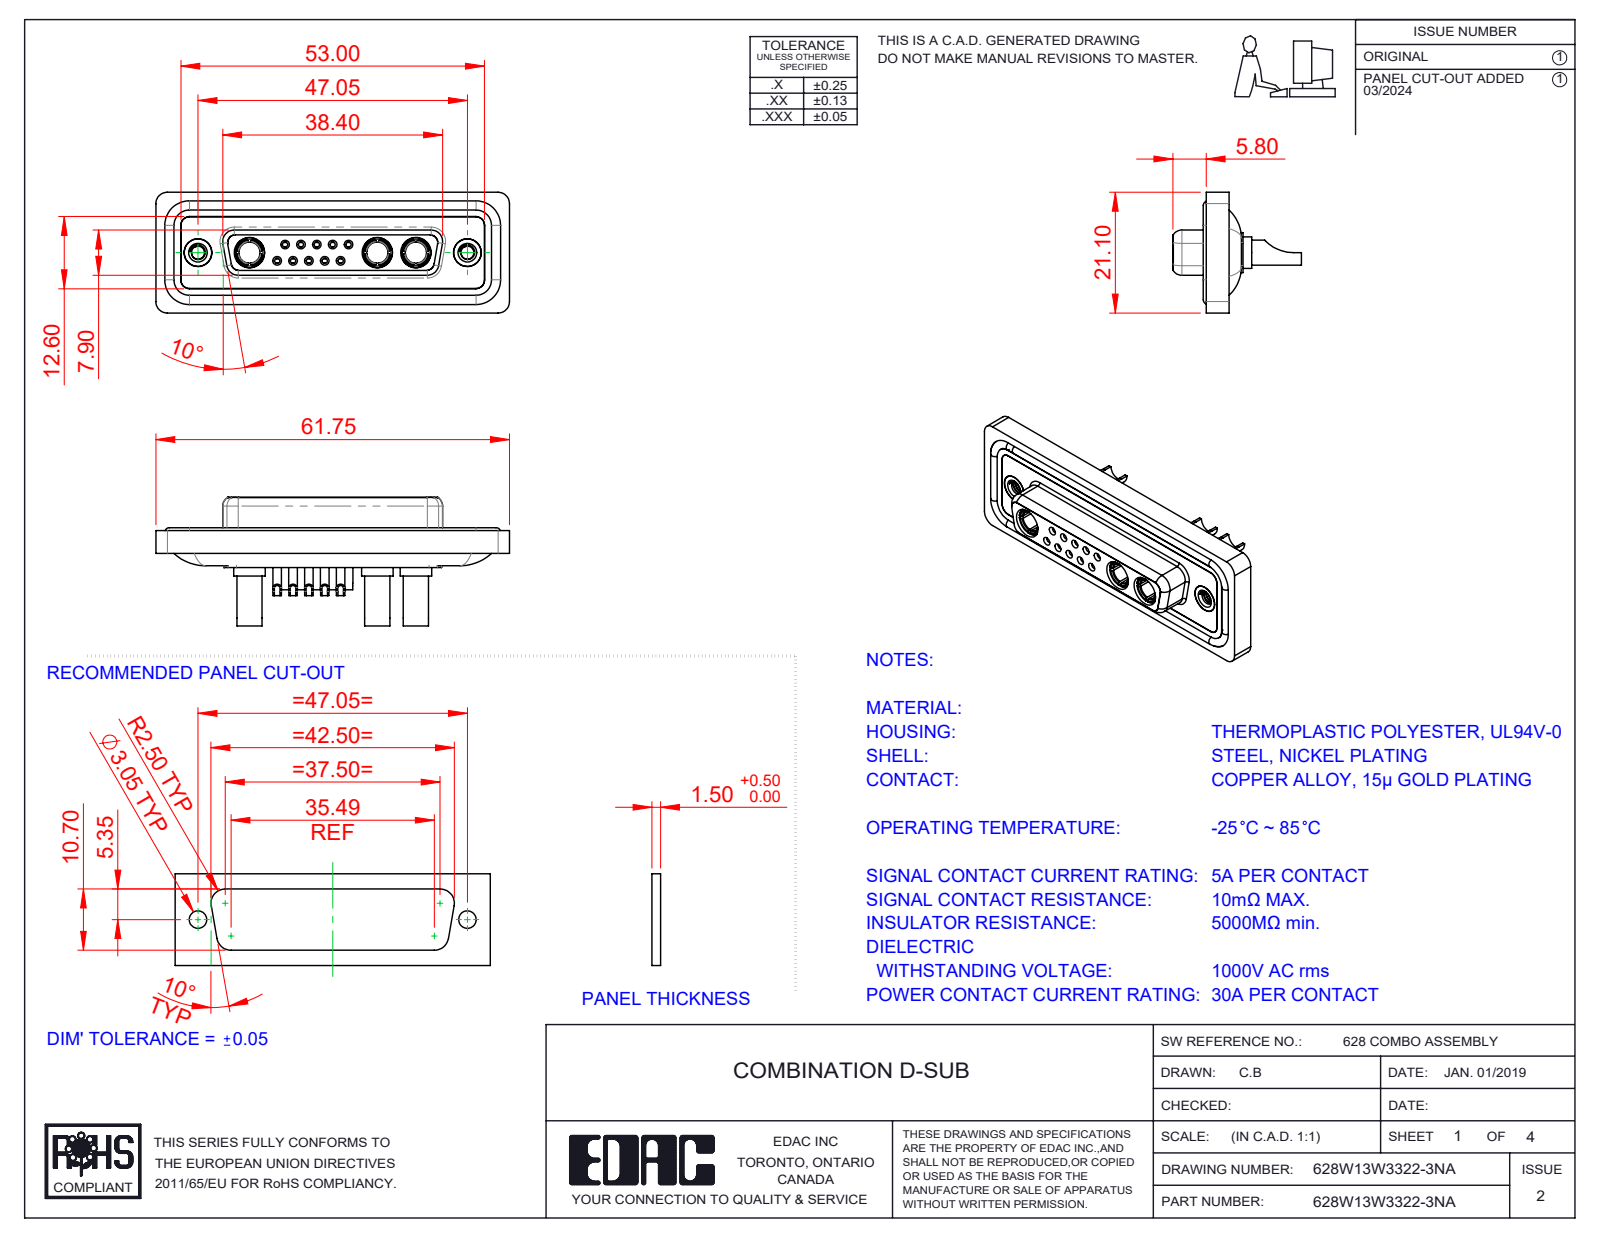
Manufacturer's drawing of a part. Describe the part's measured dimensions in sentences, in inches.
The part is named "628Combo Shell Rear_25 Contacts; Power Socket_30A SC; 628Combo Contact Row 1_22; 628Combo Housing_13W3 (+5 more)". Its 3-D file was written by "SolidWorks 2023 (CONFIG_CONTROL_DESIGN)". It is 23 solids with 1174 faces: 371 planar, 478 cylindrical and 325 other. Overall it measures 2.431 by 0.884 by 0.831 inches. Its volume is 0.511 cubic inches and its surface area 21.91 square inches. Round holes: 10 of diameter 0.035, 10 of diameter 0.039, 10 of diameter 0.043, 10 of diameter 0.059, 10 of diameter 0.079, 5 of diameter 0.063, 5 of diameter 0.067, 5 of diameter 0.191, 3 of diameter 0.138, 3 of diameter 0.146, 3 of diameter 0.209, 2 of diameter 0.089. Round bosses or shafts: 10 of diameter 0.087, 9 of diameter 0.063, 3 of diameter 0.217, 3 of diameter 0.205, 3 of diameter 0.195, 3 of diameter 0.187, 3 of diameter 0.173, 3 of diameter 0.148. Partial cylindrical surfaces (rounded edges, fillets, slot ends): 22 of radius 0.059, 18 of radius 0.079, 8 of radius 0.053, 8 of radius 0.063, 6 of radius 0.039, 4 of radius 0.01, 4 of radius 0.02, 4 of radius 0.024. The main face-to-face distances are 0.016, 0.071, 0.293, 0.222, 0.02, 0.26, 0.278, 0.063, 0.114, 0.043. The hole center spacings are 0.124, 0.109, 0.198, 0.198, 0.218, 0.327, 0.295, 0.109.
